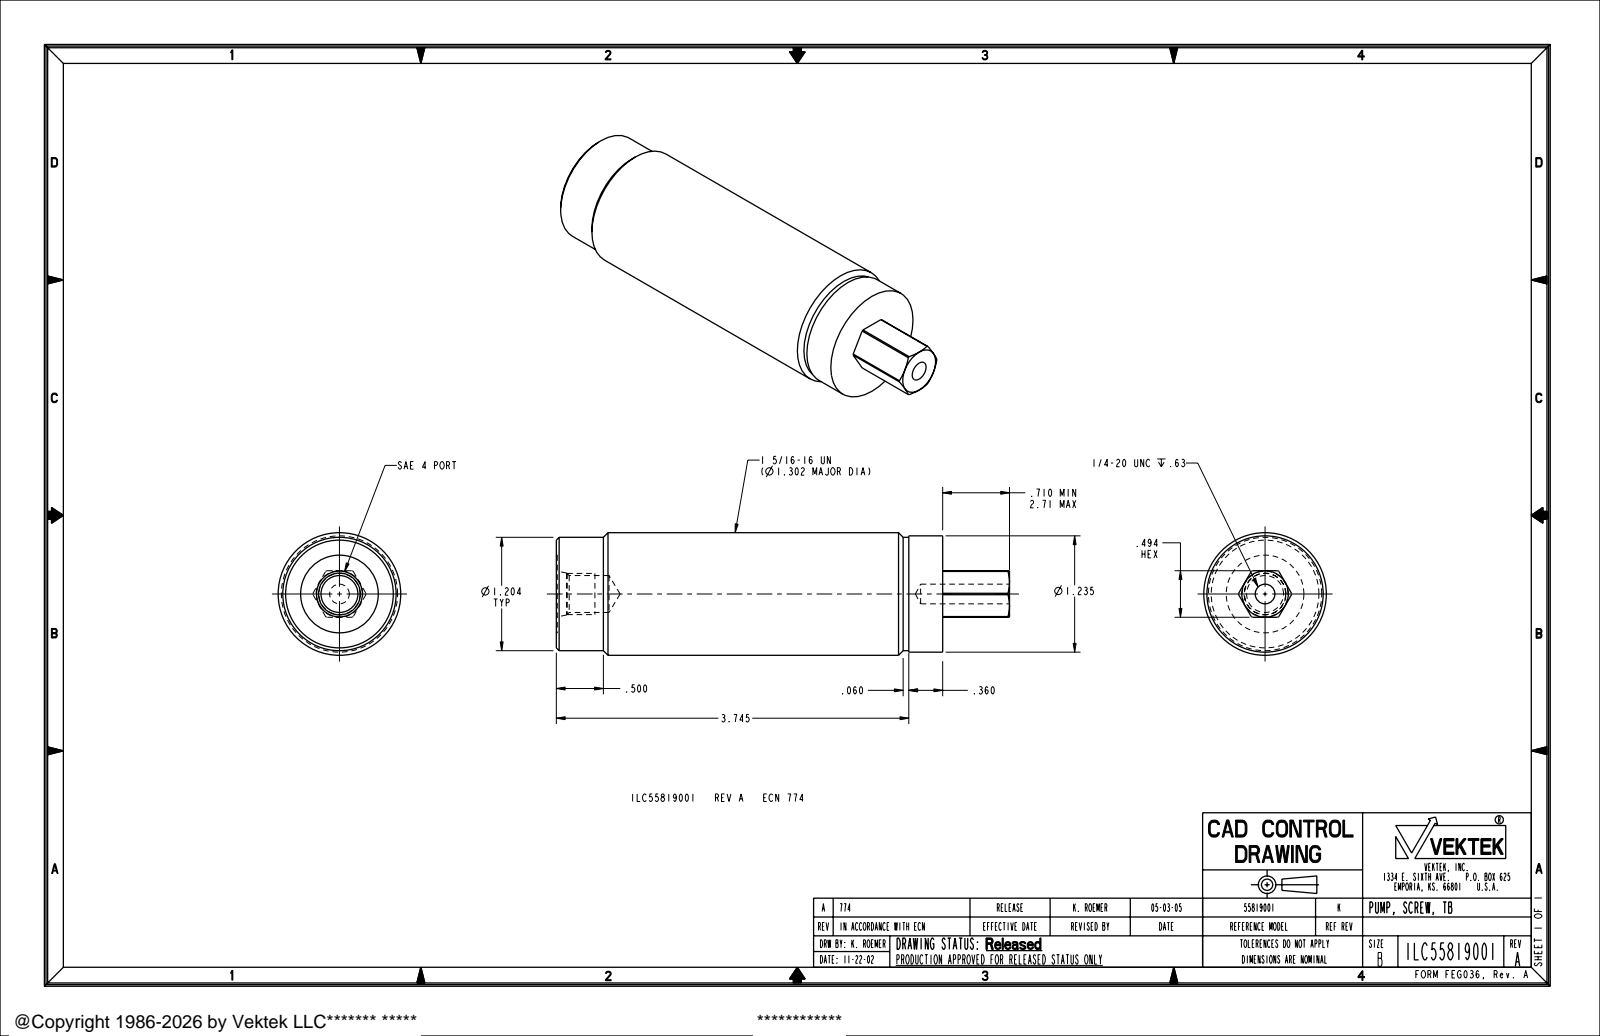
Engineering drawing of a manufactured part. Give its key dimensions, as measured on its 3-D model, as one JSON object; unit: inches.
{"part_name": "ILC55819001", "step_written_by": "PRO/ENGINEER BY PARAMETRIC TECHNOLOGY CORPORATION, 2004290 (AUTOMOTIVE_DESIGN_CC2)", "units": "inches", "bodies": {"solids": 1, "faces": 54, "planar": 12, "cylindrical": 22, "other": 20}, "overall_size": [4.815, 1.302, 1.302], "volume_in3": 5.333, "surface_area_in2": 21.97, "round_holes": [[0.209, 1], [0.392, 1], [0.825, 1]], "round_bosses_or_shafts": [[1.302, 1], [1.235, 1], [1.204, 1], [0.437, 1]], "partial_cylinders_radius": [[0.281, 1]], "face_to_face_distances": [0.494, 4.105, 4.095, 4.815, 4.805, 0.71, 3.745, 3.735, 0.36, 1.07]}
